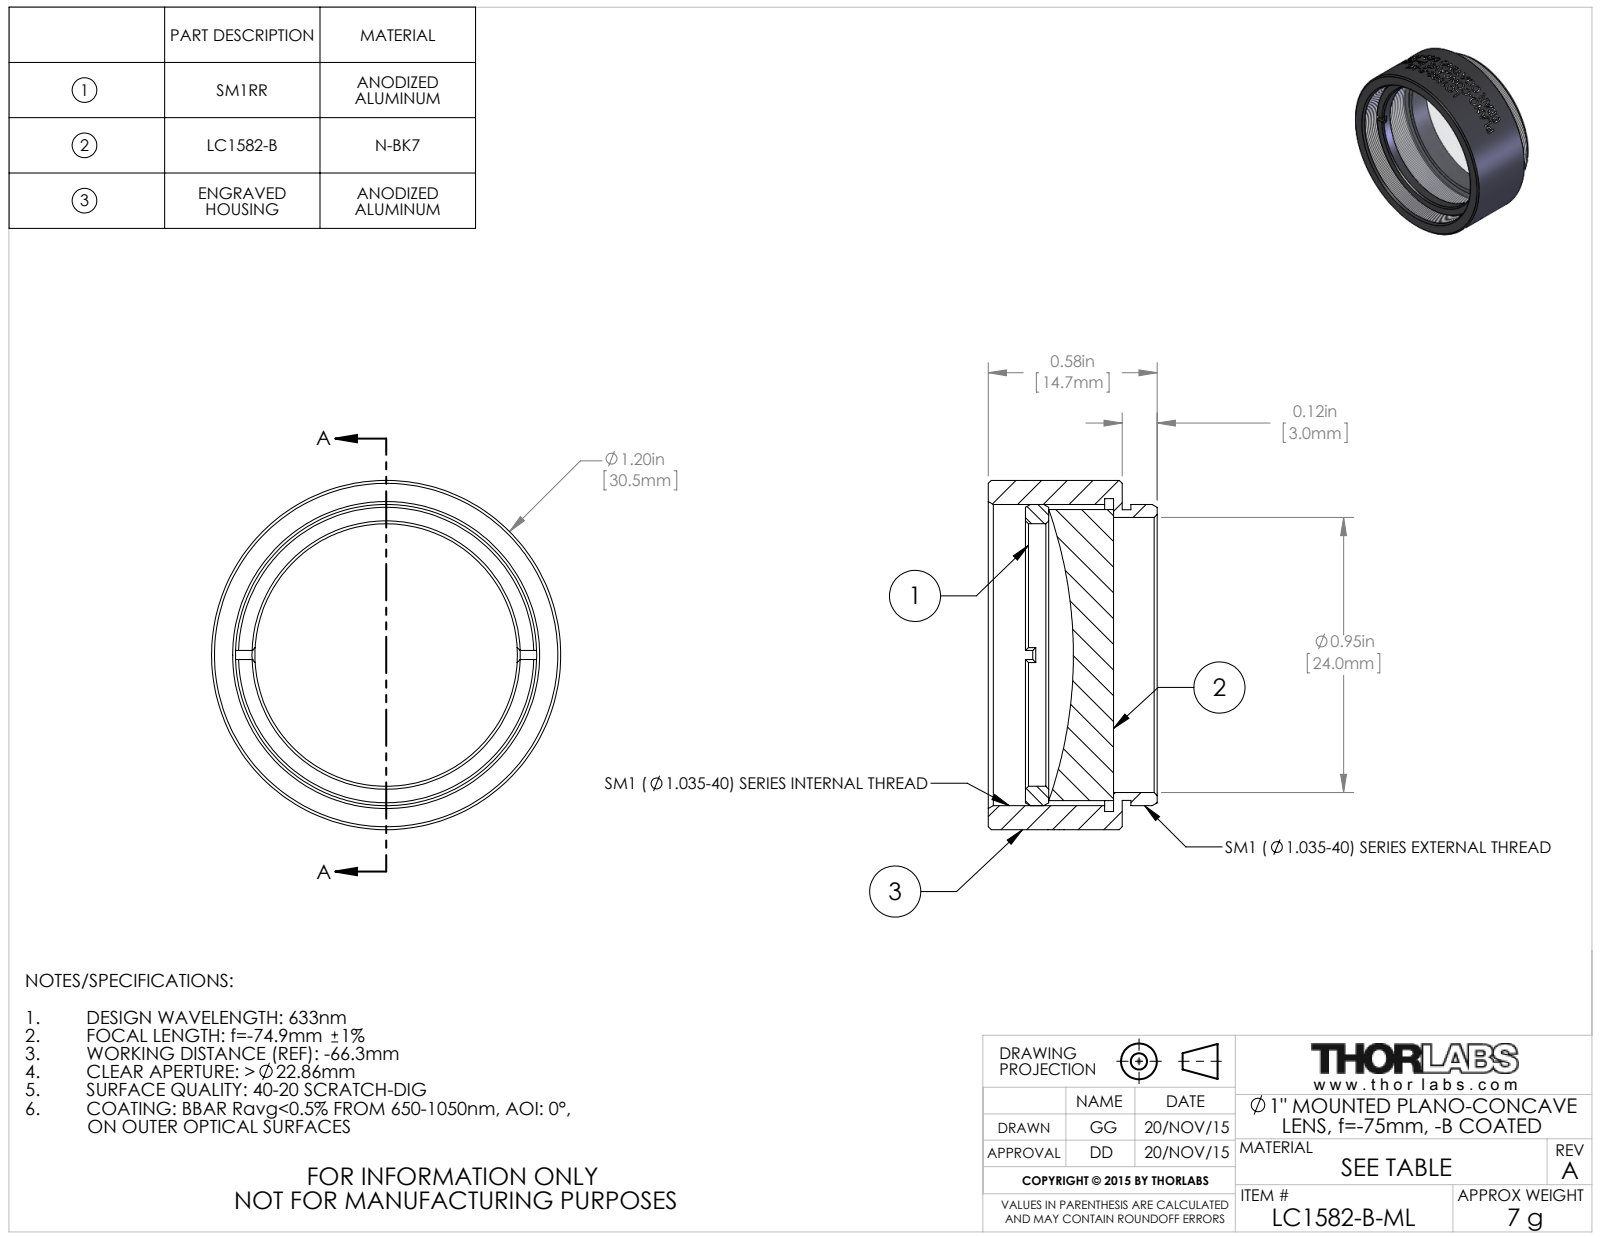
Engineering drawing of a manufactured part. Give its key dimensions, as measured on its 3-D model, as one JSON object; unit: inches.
{"part_name": "TTN045298-E0W", "step_written_by": "SolidWorks 2014 (CONFIG_CONTROL_DESIGN)", "units": "inches", "bodies": {"solids": 3, "faces": 153, "planar": 20, "cylindrical": 109, "other": 24}, "overall_size": [1.2, 1.2, 0.58], "volume_in3": 0.306, "surface_area_in2": 8.071, "round_holes": [[0.902, 1], [0.945, 1], [1.075, 1]], "round_bosses_or_shafts": [[1.2, 1], [1.035, 1], [1, 1], [0.999, 1]], "face_to_face_distances": [0.03, 0.46, 0.43, 0.252, 0.222, 0.208, 0.333, 0.303, 0.08, 0.128]}
